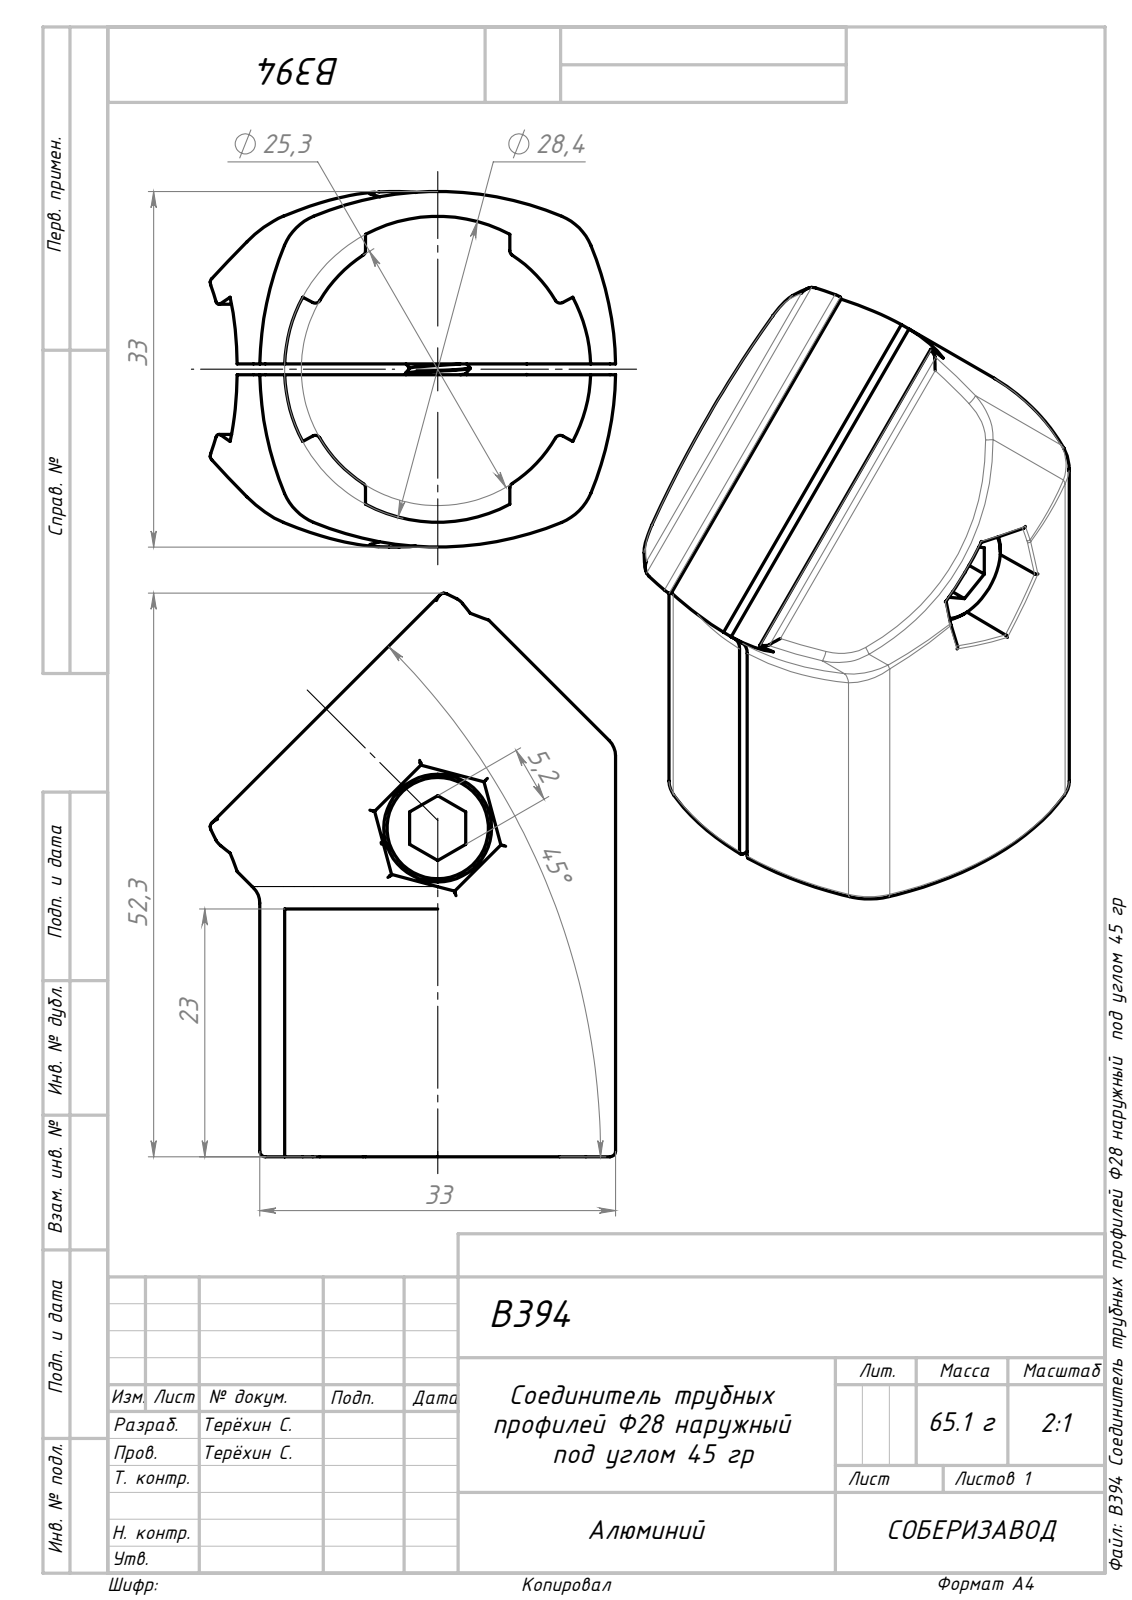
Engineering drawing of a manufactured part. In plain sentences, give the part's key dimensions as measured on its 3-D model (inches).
The part is named "B394 Соединитель трубных профилей Ф28 наружный под углом 45 гр". Its 3-D file was written by "SolidWorks 2022 (AUTOMOTIVE_DESIGN)". It is 4 solids with 357 faces: 102 planar, 132 cylindrical and 123 other. Overall it measures 2.059 by 1.481 by 1.299 inches. Its volume is 1.377 cubic inches and its surface area 20.66 square inches. Round holes: 1 of diameter 0.205, 1 of diameter 0.256, 1 of diameter 1.118. Round bosses or shafts: 1 of diameter 0.394, 1 of diameter 0.236. Partial cylindrical surfaces (rounded edges, fillets, slot ends): 22 of radius 0.02, 12 of radius 0.039, 8 of radius 0.197, 8 of radius 1.181, 2 of radius 1.083, 1 of radius 0.49, 1 of radius 0.498, 1 of radius 0.559. The main face-to-face distances are 0.039, 0.276, 0.236, 0.405, 0.551, 0.906, 0.315, 0.512, 0.787, 0.591.
